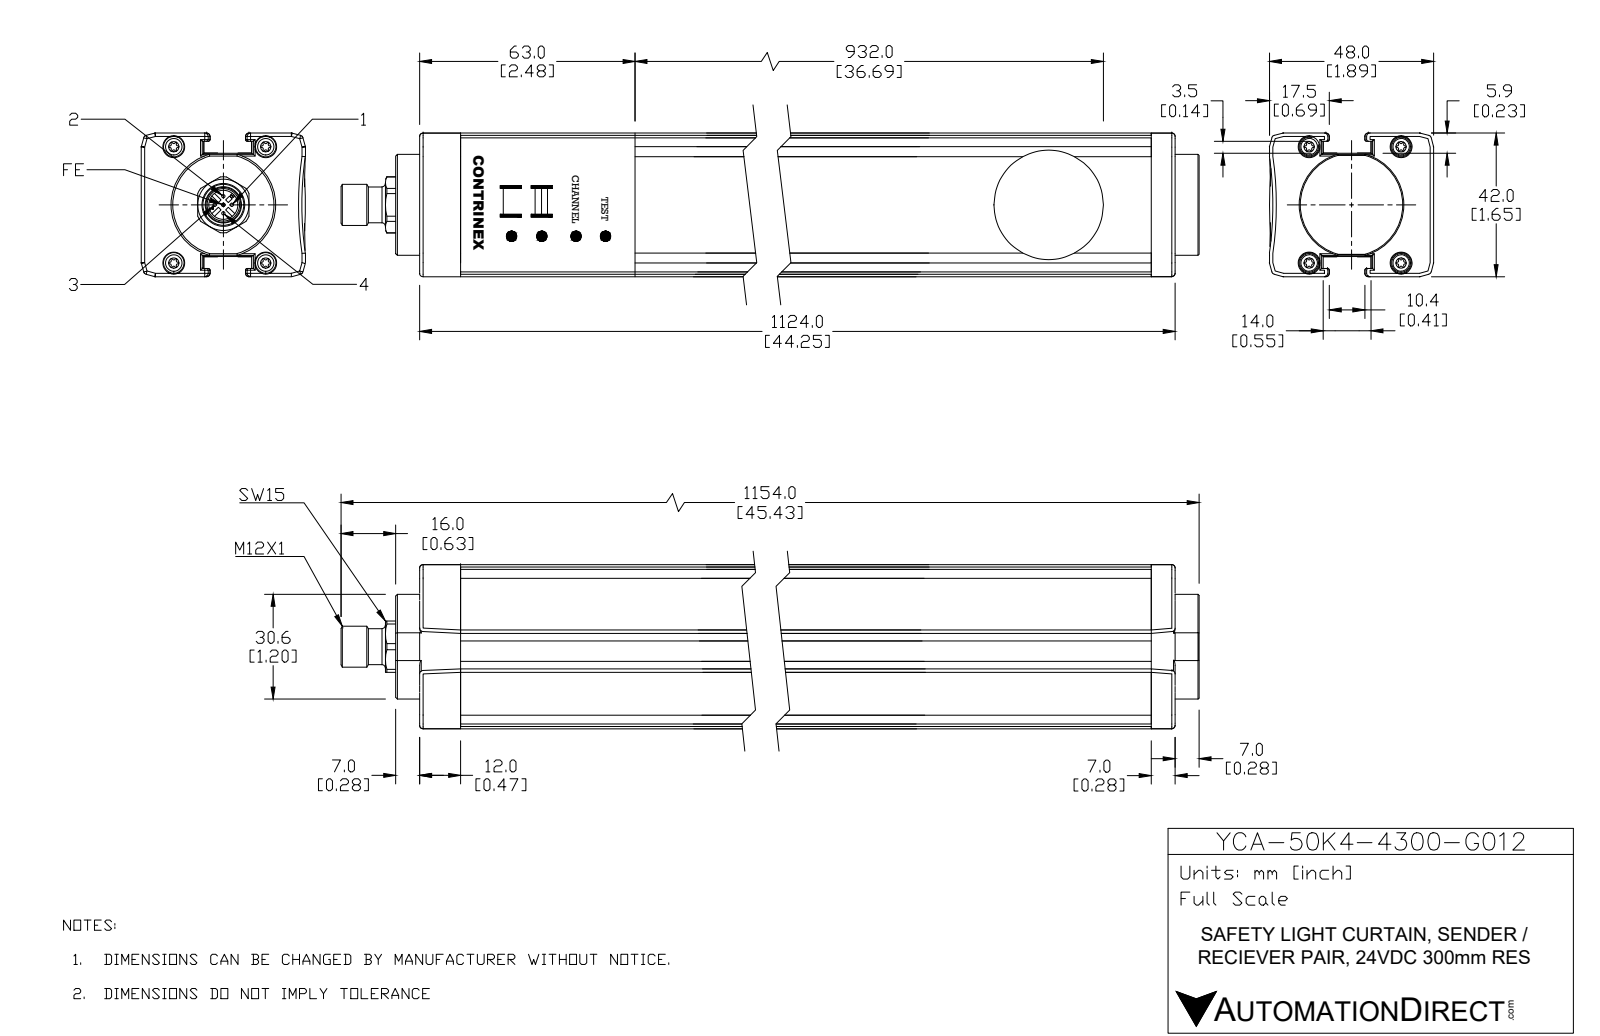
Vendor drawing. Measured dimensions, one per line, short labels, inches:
name: YCA-50K4-4300-G012
written by: SolidWorks 2019 (AUTOMOTIVE_DESIGN)
unit: in
bodies: 1 solid, 533 faces (121 planar, 152 cylindrical, 260 other)
size: 45.434 × 1.89 × 1.654
volume: 115.6 in³; area: 509.5 in²
holes: 4× ⌀0.12, 4× ⌀0.236, 1× ⌀0.335
bosses: 5× ⌀0.039, 4× ⌀0.217, 4× ⌀0.119, 1× ⌀1.205, 1× ⌀0.472, 1× ⌀0.413
rounds: 36× R0.035, 12× R0.039, 10× R0.016, 2× R0.217, 1× R0.02, 1× R0.02, 1× R0.323, 1× R0.689
face distances: 0.231, 1.422, 1.654, 1.191, 1.827, 2.172, 2.005, 0.2, 1.454, 0.031
hole spacings: 0.828, 0.88, 1.059, 1.339, 1.707
